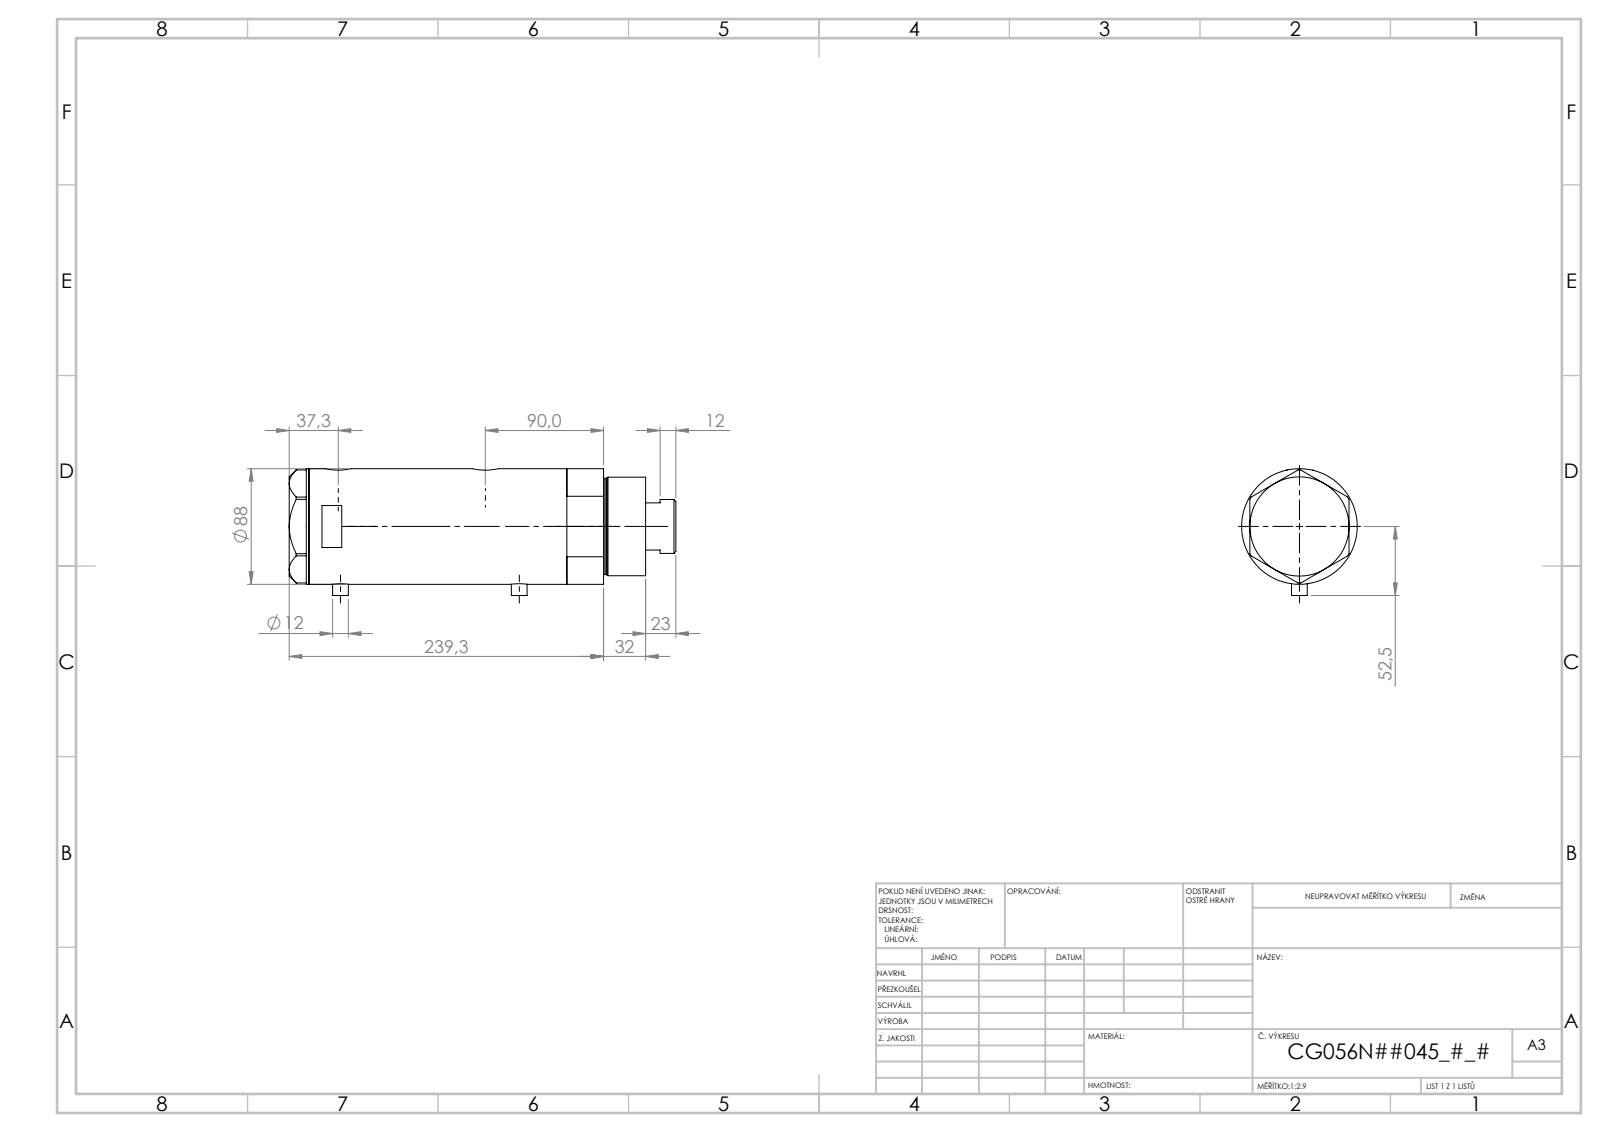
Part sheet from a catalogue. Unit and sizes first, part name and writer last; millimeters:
Units: millimetres
Overall size (bounding box): 269.47 × 89.1 × 88
Round holes (diameter × count): ⌀5 ×2, ⌀12.5 ×2, ⌀13.16 ×2, ⌀20 ×2, ⌀14.5 ×1, ⌀42 ×1, ⌀43.5 ×1, ⌀56 ×1, ⌀60 ×1, ⌀80 ×1
Round bosses / shafts (diameter × count): ⌀12 ×2, ⌀88 ×1, ⌀75 ×1, ⌀73 ×1, ⌀41 ×1
Main face-to-face distances: 119.4, 26, 93.4, 15, 41, 134.4, 231.47, 246.47, 205.47, 112.07
Hole centre spacings: 1.7, 25.8, 95.3, 97, 121.1, 122.8
Volume: 1 387 000 mm³ · Surface area: 206 555 mm²
Bodies: 4 solids, 126 faces (53 planar, 53 cylindrical, 20 other)
Part name (STEP PRODUCT): V270CG_VC; V270CG_MIDDLE; V270CG_BACK; V270CG_FRONT
STEP written by: SolidWorks 2019 (CONFIG_CONTROL_DESIGN)
